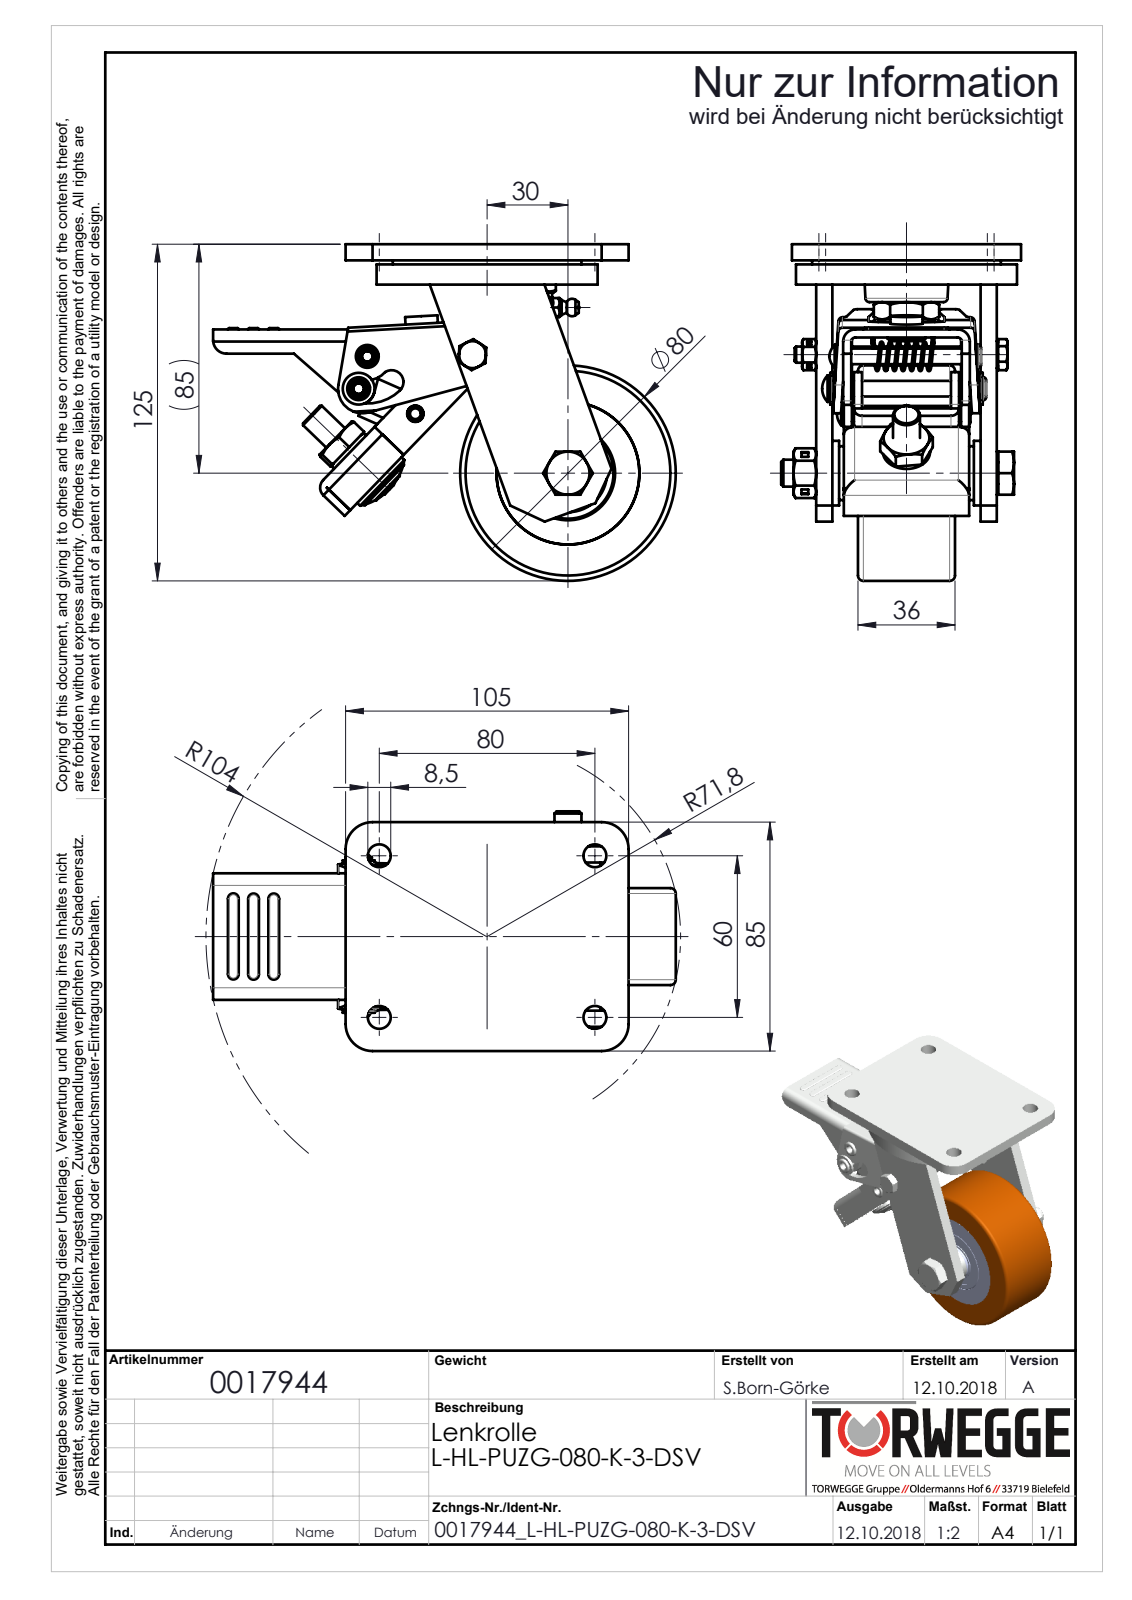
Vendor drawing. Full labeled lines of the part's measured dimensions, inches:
Part name (STEP PRODUCT): 0017944_L-HL-PUZG-080-K-3-DSV
STEP written by: SolidWorks 2018 (AUTOMOTIVE_DESIGN)
Units: inches
Bodies: 0 solids, 725 faces (264 planar, 236 cylindrical, 225 other)
Overall size (bounding box): 6.758 × 4.921 × 3.504
Round holes (diameter × count): ⌀0.335 ×5, ⌀0.236 ×4, ⌀0.197 ×2, ⌀0.33 ×2, ⌀0.63 ×2, ⌀0.157 ×1, ⌀0.228 ×1, ⌀0.244 ×1, ⌀0.248 ×1, ⌀0.256 ×1, ⌀0.315 ×1, ⌀0.394 ×1
Round bosses / shafts (diameter × count): ⌀0.827 ×2, ⌀0.394 ×2, ⌀0.039 ×2, ⌀3.228 ×1, ⌀3.15 ×1, ⌀2.756 ×1, ⌀0.945 ×1, ⌀0.929 ×1
Partial cylindrical surfaces — rounded edges, fillets, slot ends (radius × count): R0.059 ×16, R0.02 ×6, R0.039 ×4, R0.394 ×4, R0.157 ×3, R0.118 ×2, R0.173 ×2, R0.177 ×2
Main face-to-face distances: 0.236, 0.118, 1.791, 0.61, 0.374, 2.028, 2.402, 0.591, 0.354, 1.417
Hole centre spacings: 1.969, 1.398, 2.362, 2.676, 3.15, 3.937, 0.489, 0.827
